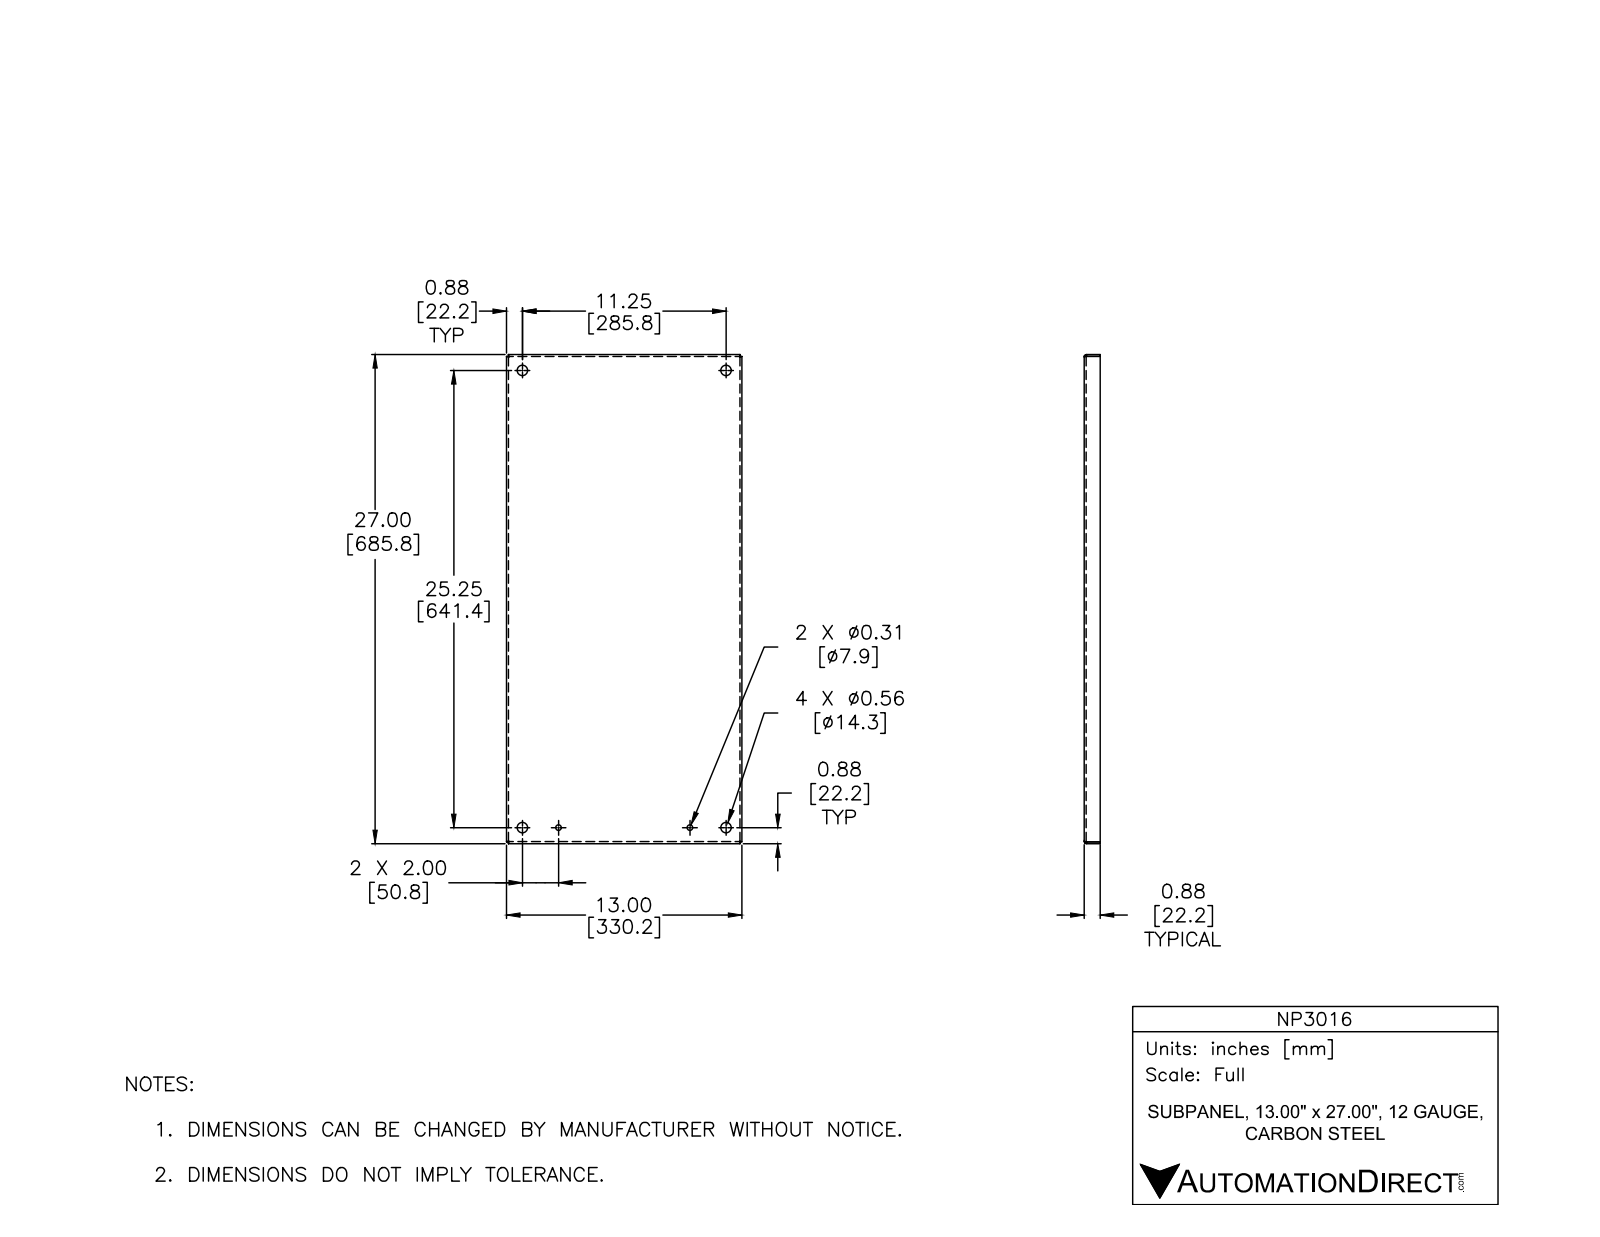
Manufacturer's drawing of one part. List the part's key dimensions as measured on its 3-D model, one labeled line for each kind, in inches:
Part name (STEP PRODUCT): NP3016
STEP written by: Autodesk Inventor 2012 (AUTOMOTIVE_DESIGN)
Units: inches
Bodies: 1 solid, 44 faces (22 planar, 14 cylindrical, 8 other)
Overall size (bounding box): 27 × 13 × 0.875
Volume: 38.34 in³ · Surface area: 826.9 in²
Round holes (diameter × count): ⌀0.563 ×4, ⌀0.312 ×2
Partial cylindrical surfaces — rounded edges, fillets, slot ends (radius × count): R0.031 ×4, R0.125 ×4
Main face-to-face distances: 0.094, 12.906, 13, 12.813, 26.906, 27, 26.813, 0.781, 0.875, 0.105
Hole centre spacings: 2, 9.25, 11.25, 25.25, 25.329, 26.891, 27.643, 7.25
